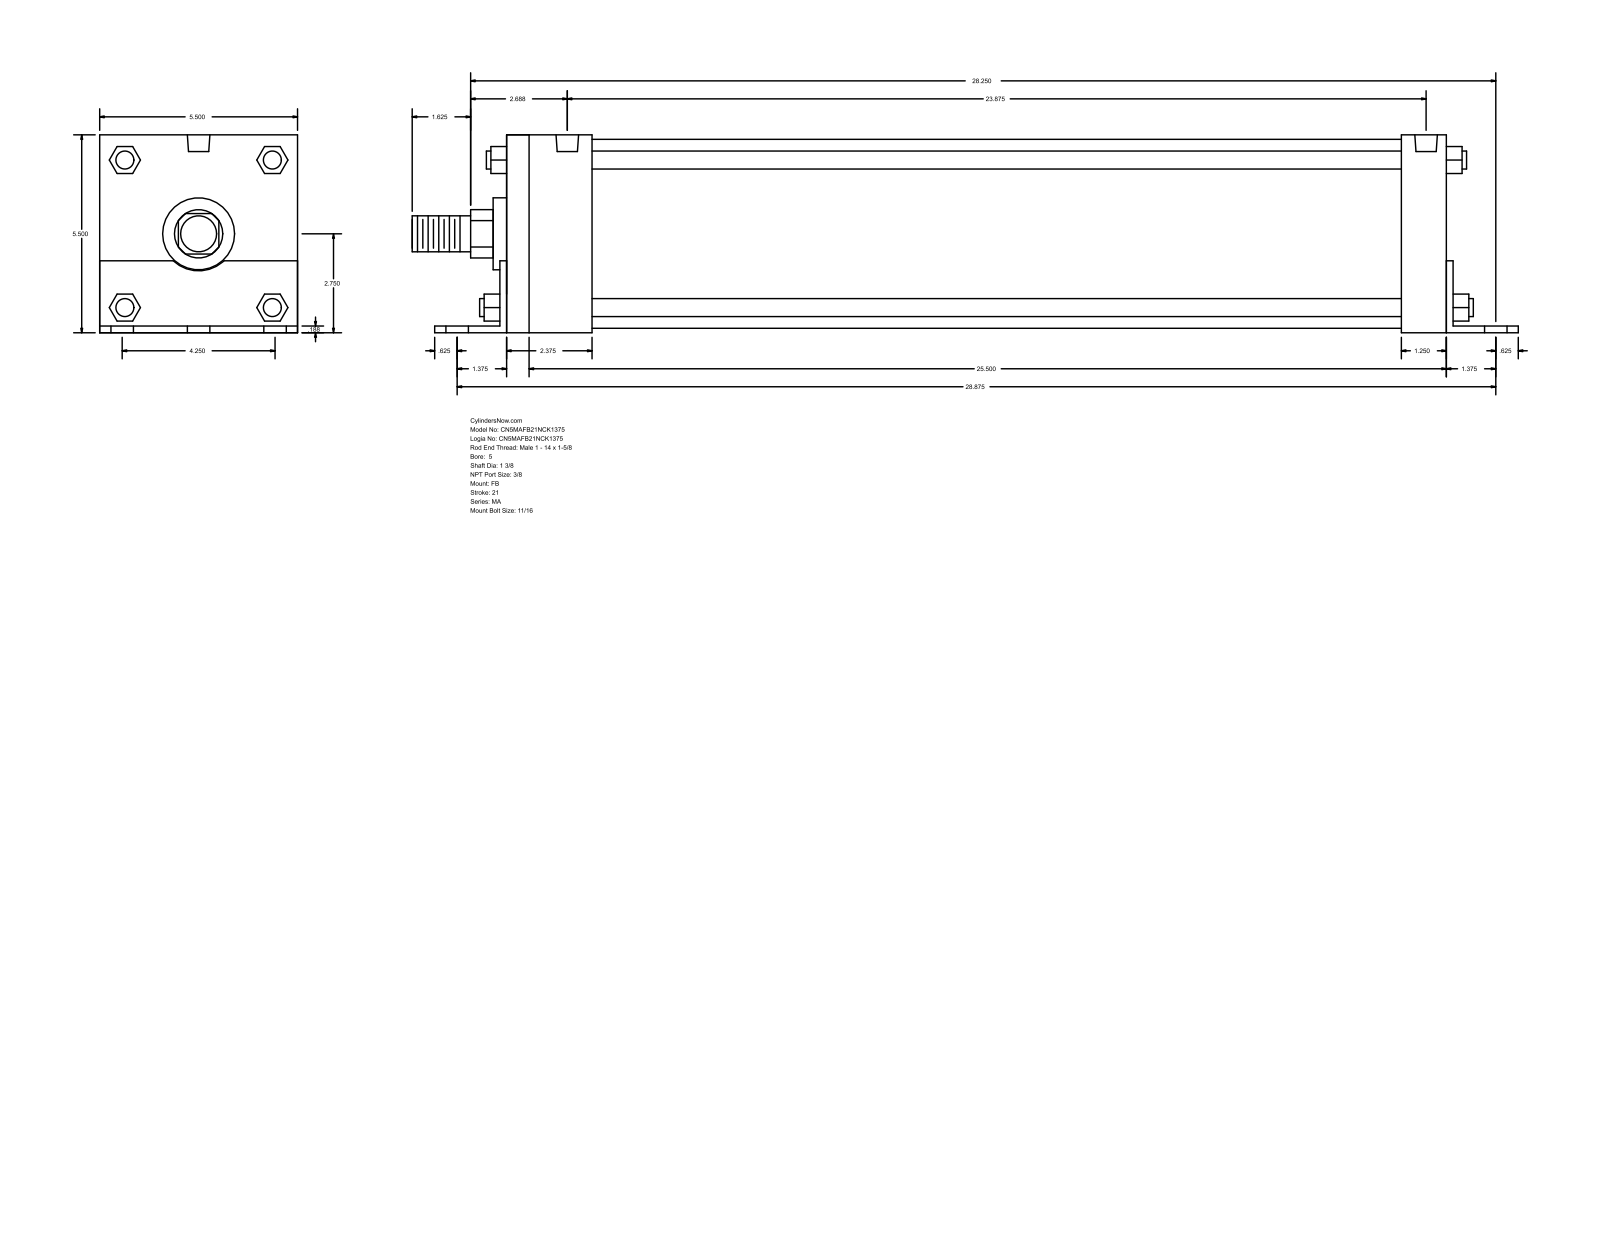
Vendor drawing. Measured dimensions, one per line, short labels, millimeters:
name: MA_FB__0500_1.375
written by: GSSL Pune (CONFIG_CONTROL_DESIGN)
unit: mm
bodies: 0 solids, 140 faces (105 planar, 35 cylindrical, 0 other)
size: 781.05 × 139.75 × 139.7
holes: 6× ⌀17.46, 4× ⌀11.11, 2× ⌀15.93
bosses: 4× ⌀12.7, 1× ⌀133.35, 1× ⌀50.8, 1× ⌀34.92, 1× ⌀25.4
rounds: 1× R17.06, 1× R26.16
face distances: 139.7, 4.76, 139.75, 668.34, 4.71, 134.99, 663.58, 673.1, 31.75, 36.51
hole spacings: 53.98, 735.41, 733.43, 4.77, 73.04, 76.34, 94.68, 98.64
